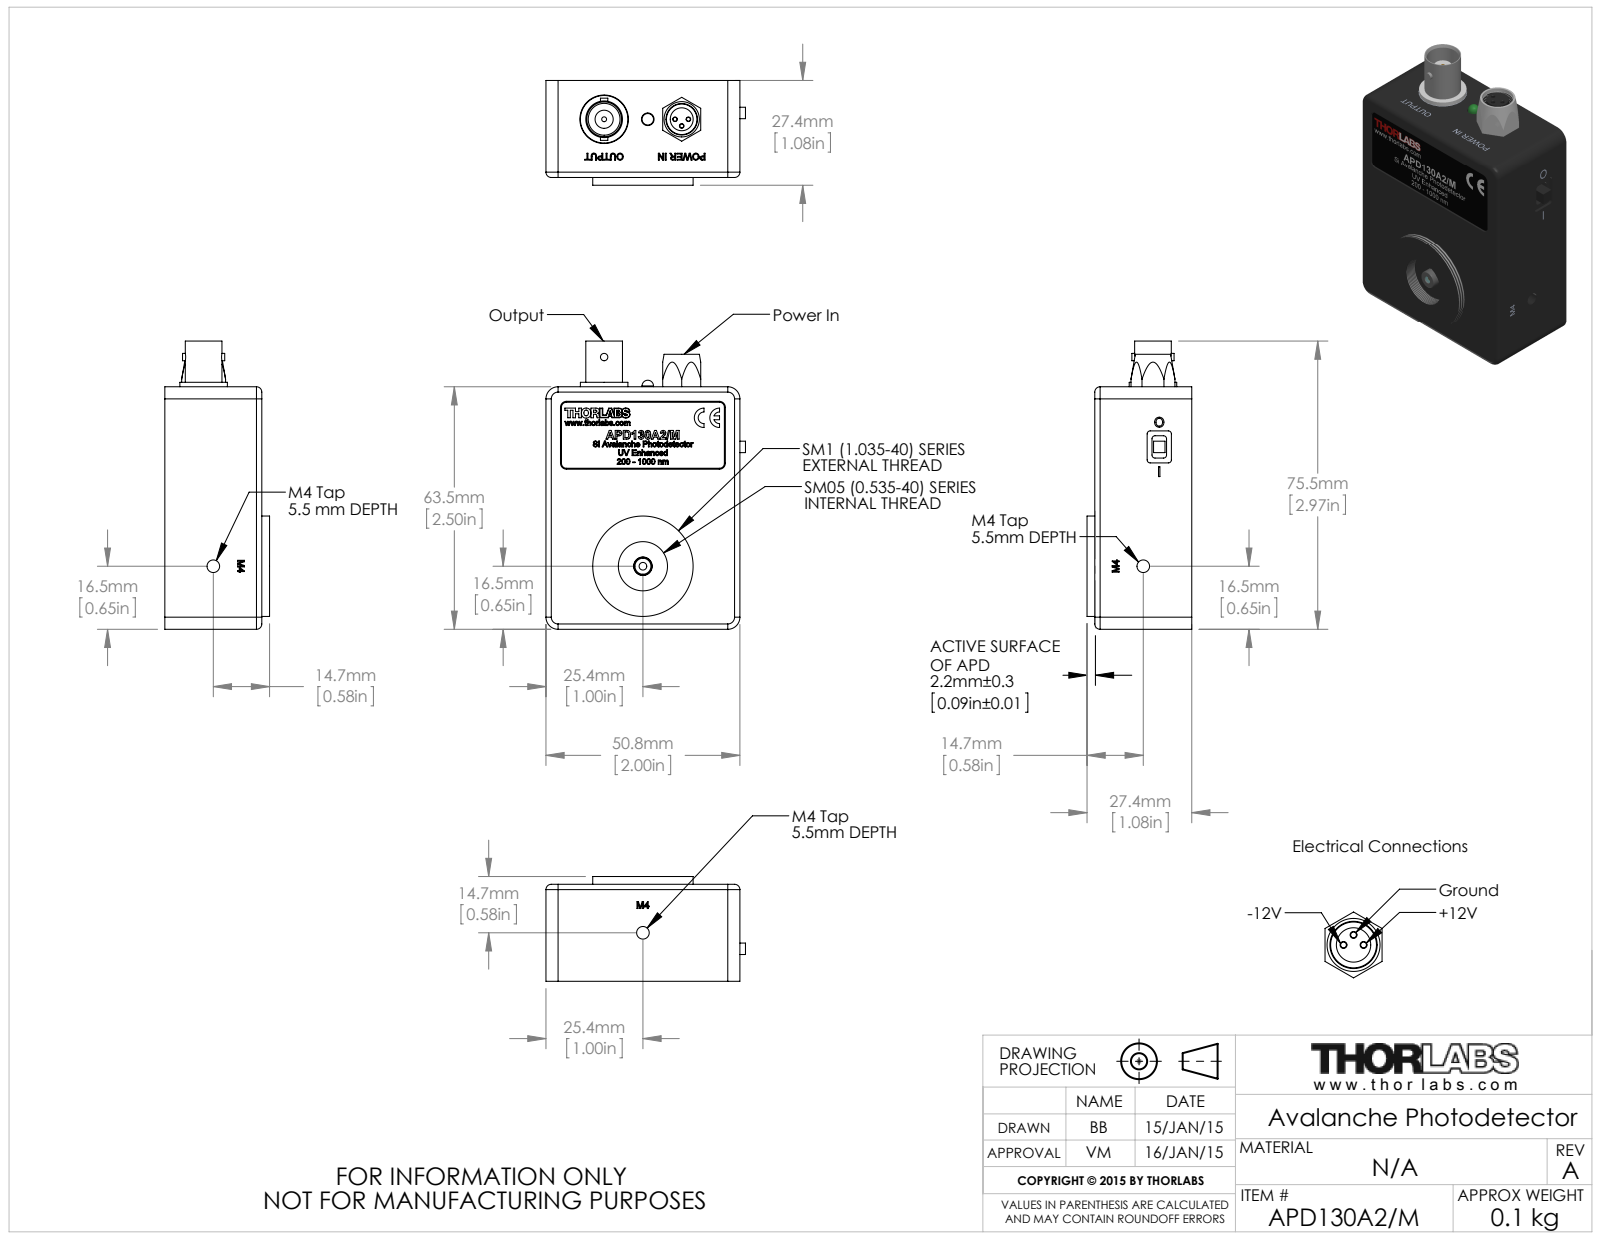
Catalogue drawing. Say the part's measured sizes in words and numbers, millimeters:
The part is named "MTN004762-E0W". Its 3-D file was written by "SolidWorks 2014 (AUTOMOTIVE_DESIGN)". It is 12 solids with 2054 faces: 1099 planar, 252 cylindrical and 703 other. Overall it measures 75.46 by 52.26 by 27.43 millimeters. Its volume is 36 153 cubic millimeters and its surface area 28 859 square millimeters. Round holes: 8 of diameter 1.6, 4 of diameter 2.4, 3 of diameter 1, 3 of diameter 1.02, 2 of diameter 3.3, 1 of diameter 1.27, 1 of diameter 1.32, 1 of diameter 2, 1 of diameter 2.5, 1 of diameter 3.3, 1 of diameter 4.14, 1 of diameter 4.85. Round bosses or shafts: 6 of diameter 0.51, 5 of diameter 3.8, 4 of diameter 2, 3 of diameter 0.45, 1 of diameter 26.29, 1 of diameter 12.45, 1 of diameter 10.92, 1 of diameter 9.6. Partial cylindrical surfaces (rounded edges, fillets, slot ends): 18 of radius 3.17, 14 of radius 3.3, 8 of radius 0.79, 8 of radius 1.91, 8 of radius 2.41, 5 of radius 2.54, 4 of radius 1.27, 4 of radius 1.4. The main face-to-face distances are 1.59, 2.54, 25.4, 23.81, 1.14, 0.51, 24.89, 23.3, 1.65, 23.75. The hole center spacings are 4.41, 41.17, 51.14, 65.51, 1.27, 1.75, 1.8, 2.47.
